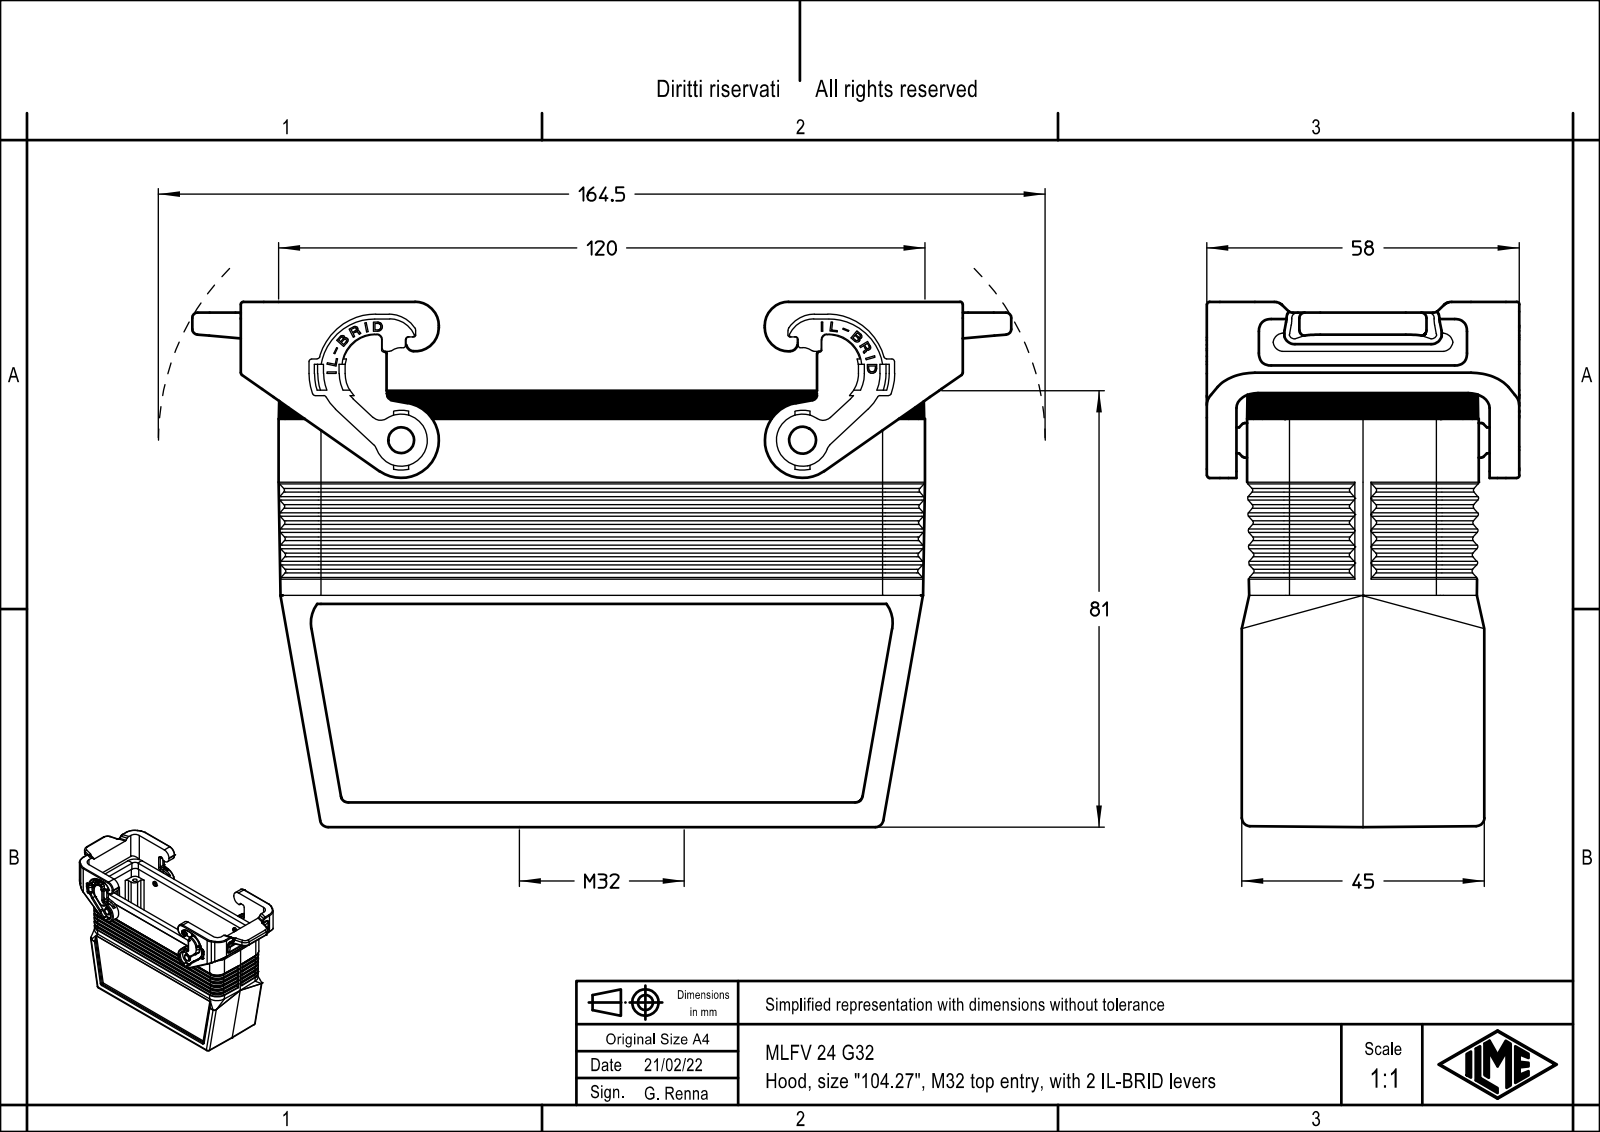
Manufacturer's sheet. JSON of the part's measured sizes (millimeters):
{"part_name": "MLFV_24_G32", "step_written_by": "Creo Elements/Direct Modeling 20.1B 02-Apr-2019 (C) Parametric Technology GmbH (AUTOMOTIVE_DESIGN)", "units": "millimeters", "bodies": {"solids": 1, "faces": 1599, "planar": 1028, "cylindrical": 391, "other": 180}, "overall_size": [152, 97.45, 58], "volume_mm3": 137927, "surface_area_mm2": 71875, "round_holes": [[2.75, 4], [30.6, 1]], "round_bosses_or_shafts": [[6.8, 2], [4.8, 2]], "partial_cylinders_radius": [[0.5, 104], [1, 46], [3, 20], [7, 16], [0.33, 15], [1.5, 14], [0.3, 8], [2, 8]], "face_to_face_distances": [39.25, 3.75, 2, 1, 4.75, 43, 5.75, 34.5, 38.25, 35.5], "hole_center_spacings": [53.72, 27, 104, 107.45]}
